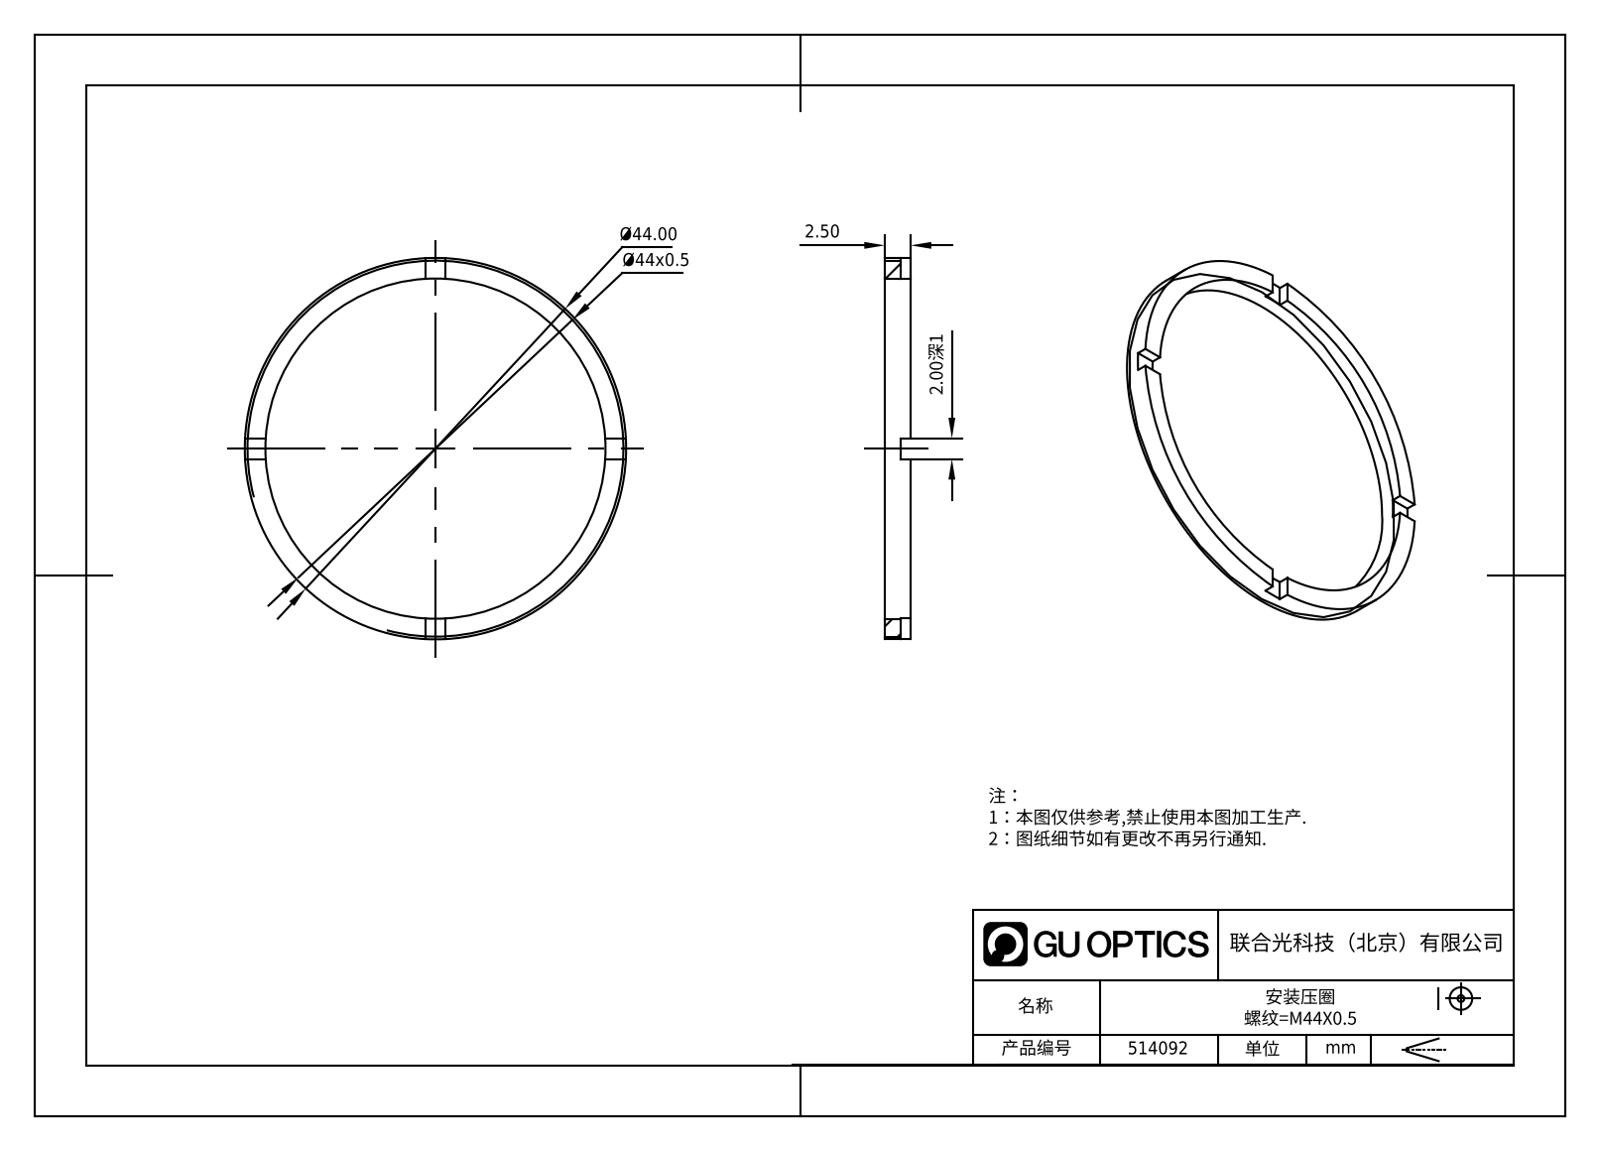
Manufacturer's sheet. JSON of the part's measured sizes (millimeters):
{"part_name": "514092", "step_written_by": "SolidWorks 2020 (CONFIG_CONTROL_DESIGN)", "units": "millimeters", "bodies": {"solids": 1, "faces": 21, "planar": 17, "cylindrical": 4, "other": 0}, "overall_size": [44, 44, 2.5], "volume_mm3": 644, "surface_area_mm2": 1188, "round_holes": [[40, 1]], "round_bosses_or_shafts": [[44, 1]], "face_to_face_distances": [2.5, 1.5, 1, 2]}
